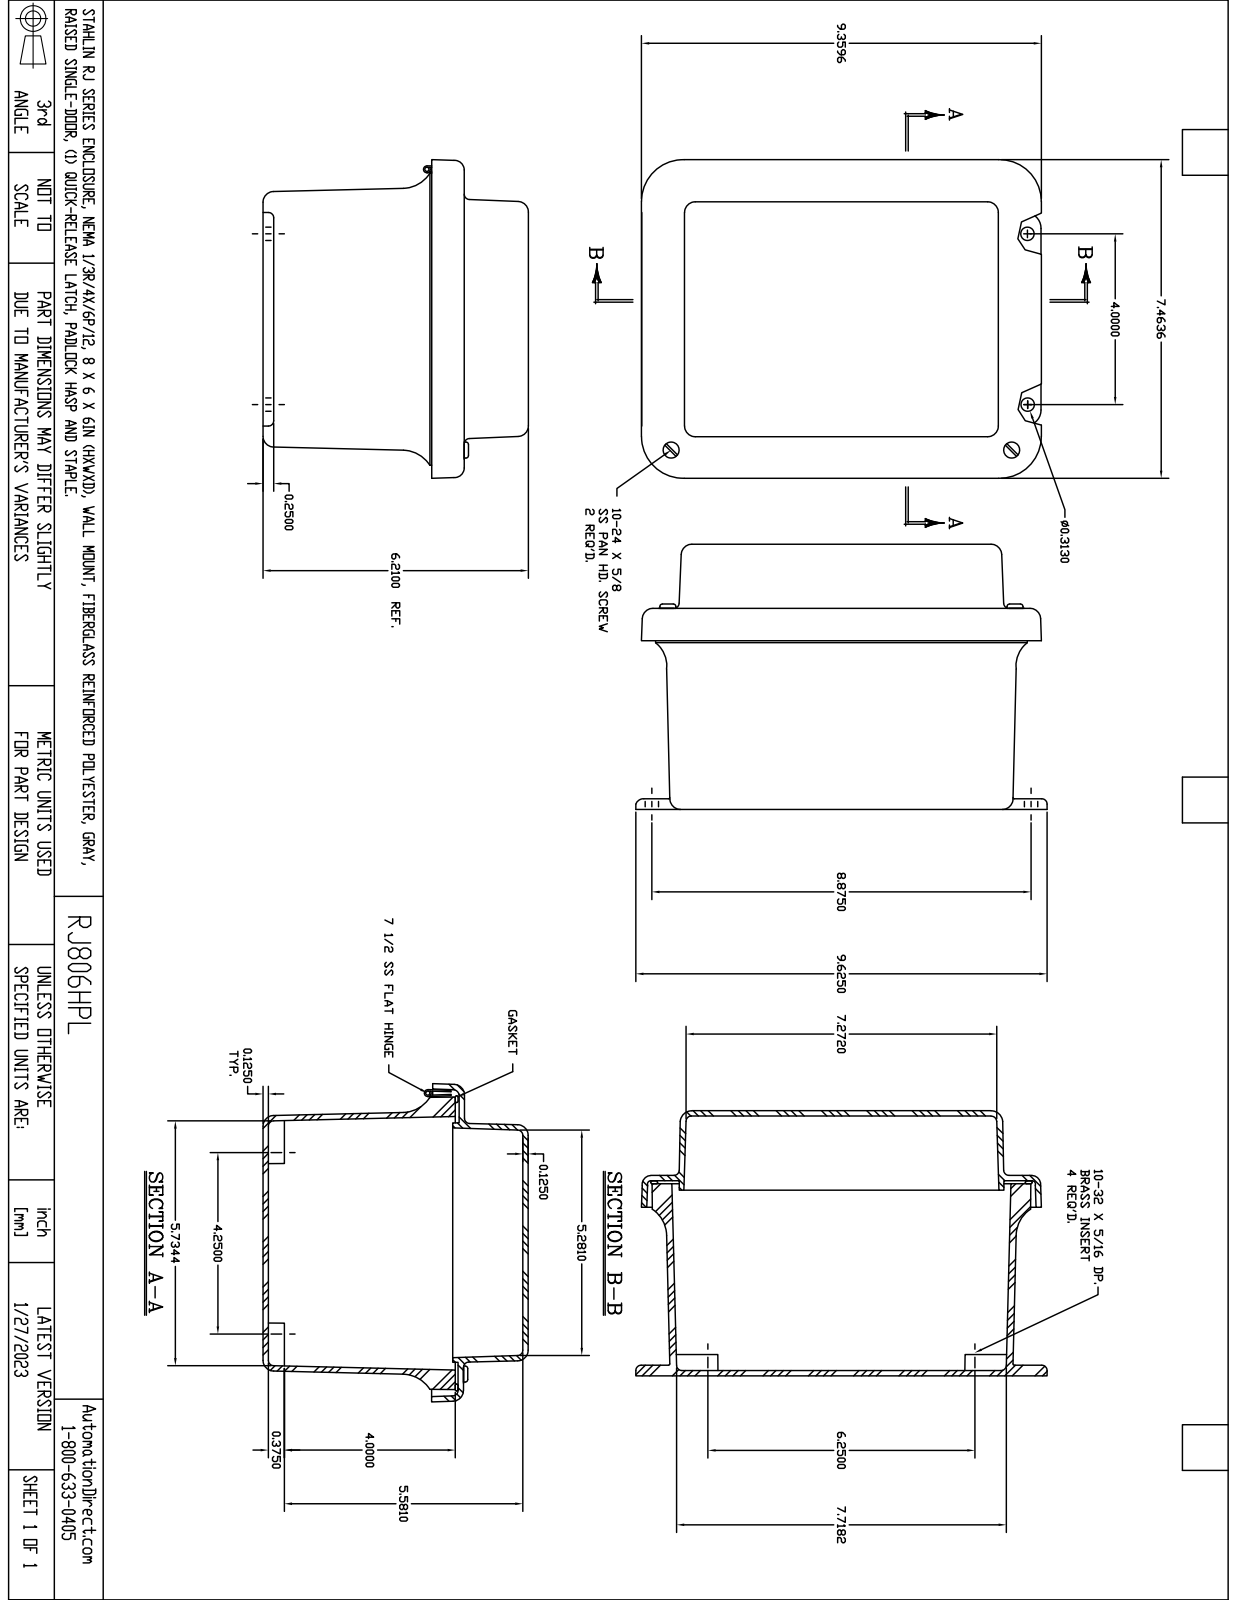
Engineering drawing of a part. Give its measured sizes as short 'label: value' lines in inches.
name: MR806HPL
written by: SolidWorks 2018 (AUTOMOTIVE_DESIGN)
unit: in
bodies: 25 solids, 745 faces (301 planar, 292 cylindrical, 152 other)
size: 9.625 × 7.553 × 6.215
volume: 48.69 in³; area: 689.5 in²
holes: 12× ⌀0.14, 6× ⌀0.131, 5× ⌀0.152, 4× ⌀0.104, 4× ⌀0.156, 4× ⌀0.218, 2× ⌀0.13, 2× ⌀0.135, 1× ⌀0.085, 1× ⌀0.085, 1× ⌀0.135, 1× ⌀0.375
bosses: 5× ⌀0.25, 5× ⌀0.125, 4× ⌀0.27, 4× ⌀0.125, 1× ⌀0.3, 1× ⌀0.17, 1× ⌀0.155, 1× ⌀0.155
rounds: 24× R0.125, 20× R0.031, 12× R0.015, 12× R0.25, 8× R0.045, 6× R0.03, 4× R0.022, 4× R0.06
face distances: 0.125, 0.125, 1.515, 5.965, 4.45, 6.09, 6.215, 6.089, 4.575, 1.64
hole spacings: 3.5, 0.25, 0.75, 0.937, 1.326, 5.271, 7.249, 8.864
